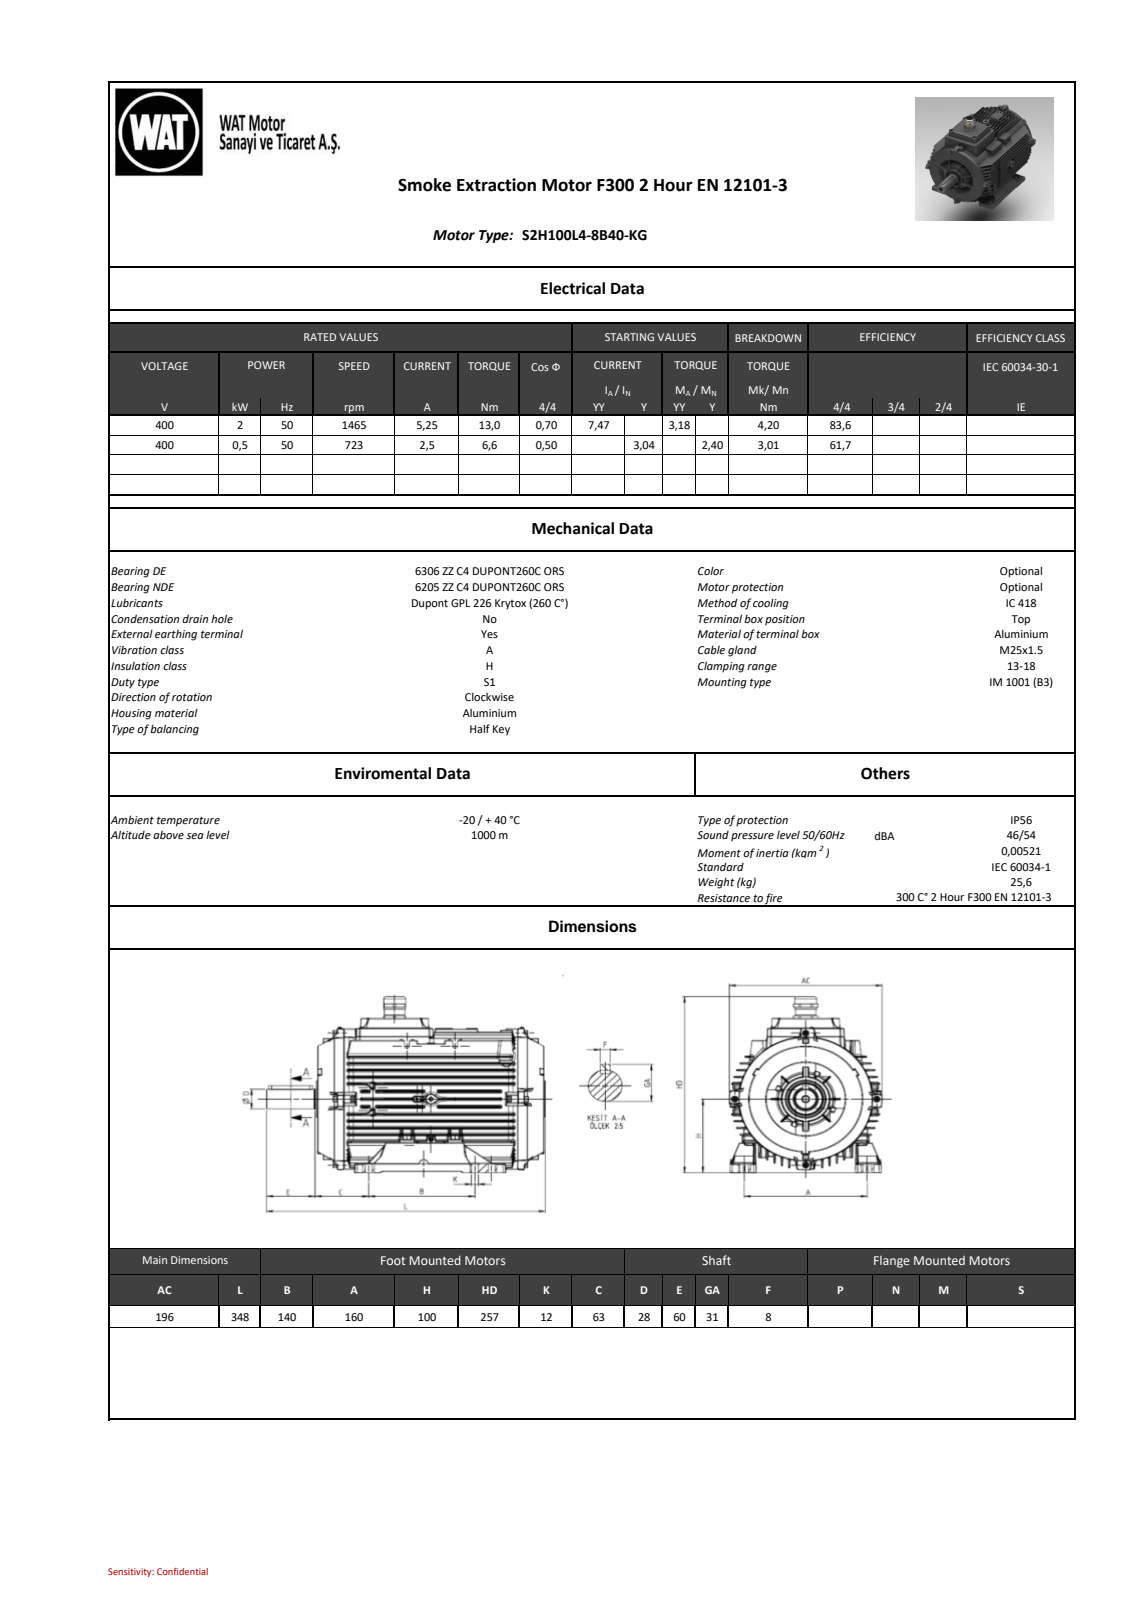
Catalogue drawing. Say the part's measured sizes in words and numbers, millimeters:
The part is named "260314206C66ebe1". Its 3-D file was written by "SIEMENS PLM Software NX 11.0 (AP203_CONFIGURATION_CONTROLLED_3D_DESIGN_OF_MECHANICAL_PARTS_AND_ASSEMBLIES_MIM_LF)". It is 0 solids with 6364 faces: 1240 planar, 1855 cylindrical and 3269 other. Overall it measures 348 by 257.2 by 196 millimeters. Round holes: 8 of diameter 6.5, 1 of diameter 8.5, 1 of diameter 10.5, 1 of diameter 18, 1 of diameter 32, 1 of diameter 40, 1 of diameter 43.9, 1 of diameter 44.1. Round bosses or shafts: 4 of diameter 9.2, 4 of diameter 8.5, 4 of diameter 8, 4 of diameter 5, 1 of diameter 168, 1 of diameter 30, 1 of diameter 29.59, 1 of diameter 28.14. Partial cylindrical surfaces (rounded edges, fillets, slot ends): 619 of radius 0.8, 301 of radius 1, 140 of radius 2, 94 of radius 0.5, 85 of radius 1.5, 59 of radius 0.81, 16 of radius 2.5, 16 of radius 4.5. The main face-to-face distances are 8.53, 8.46, 8.45, 76.24, 16.91, 93.45, 76.68, 17.05, 25.58, 59.63. The hole center spacings are 10, 64, 128, 128.39, 143.11, 54, 64.56, 66.62.
